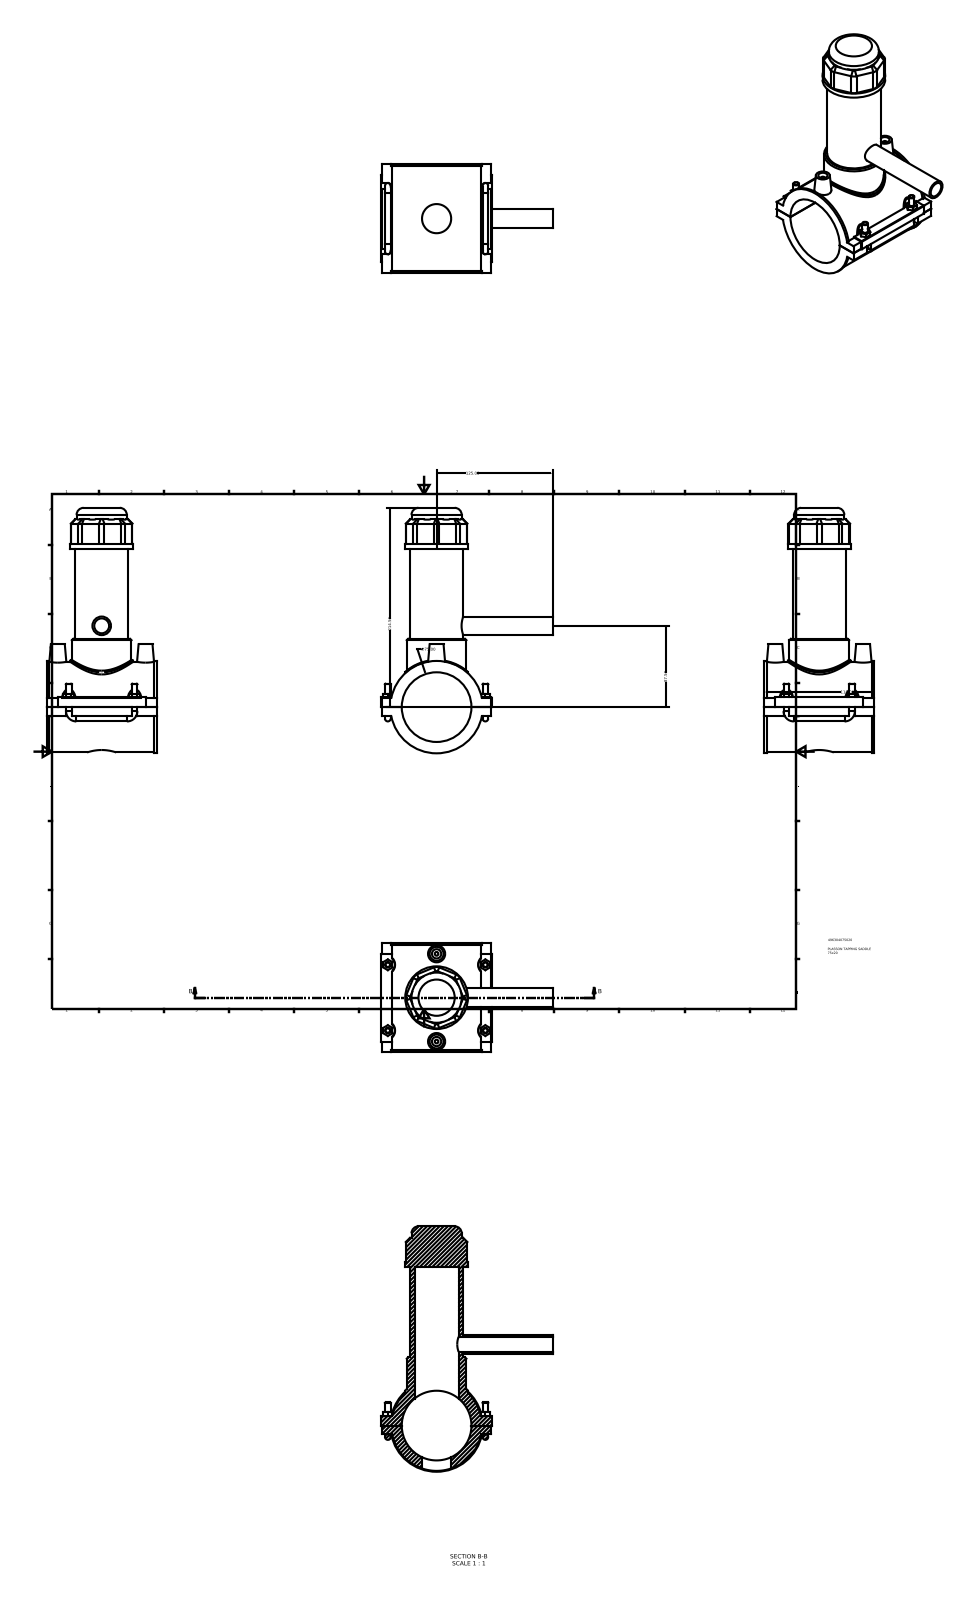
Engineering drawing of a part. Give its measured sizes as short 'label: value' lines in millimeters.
name: 496304075020
written by: Autodesk Inventor 2015 (CONFIG_CONTROL_DESIGN)
unit: mm
bodies: 1 solid, 192 faces (118 planar, 49 cylindrical, 25 other)
size: 264.23 × 184.5 × 118
volume: 653 880 mm³; area: 157 988 mm²
holes: 2× ⌀10, 1× ⌀16, 1× ⌀31.36, 1× ⌀47.25, 1× ⌀75
bosses: 6× ⌀6, 2× ⌀4, 1× ⌀99.45, 1× ⌀97.5, 1× ⌀67.5, 1× ⌀64.12, 1× ⌀57.38, 1× ⌀54
rounds: 12× R7.5, 4× R3, 1× R0.5, 1× R50.7
face distances: 118, 170.3, 170.2, 9.33, 9.43, 1, 179.63, 19.76, 10.43, 10.33
hole spacings: 47.2, 94.4
